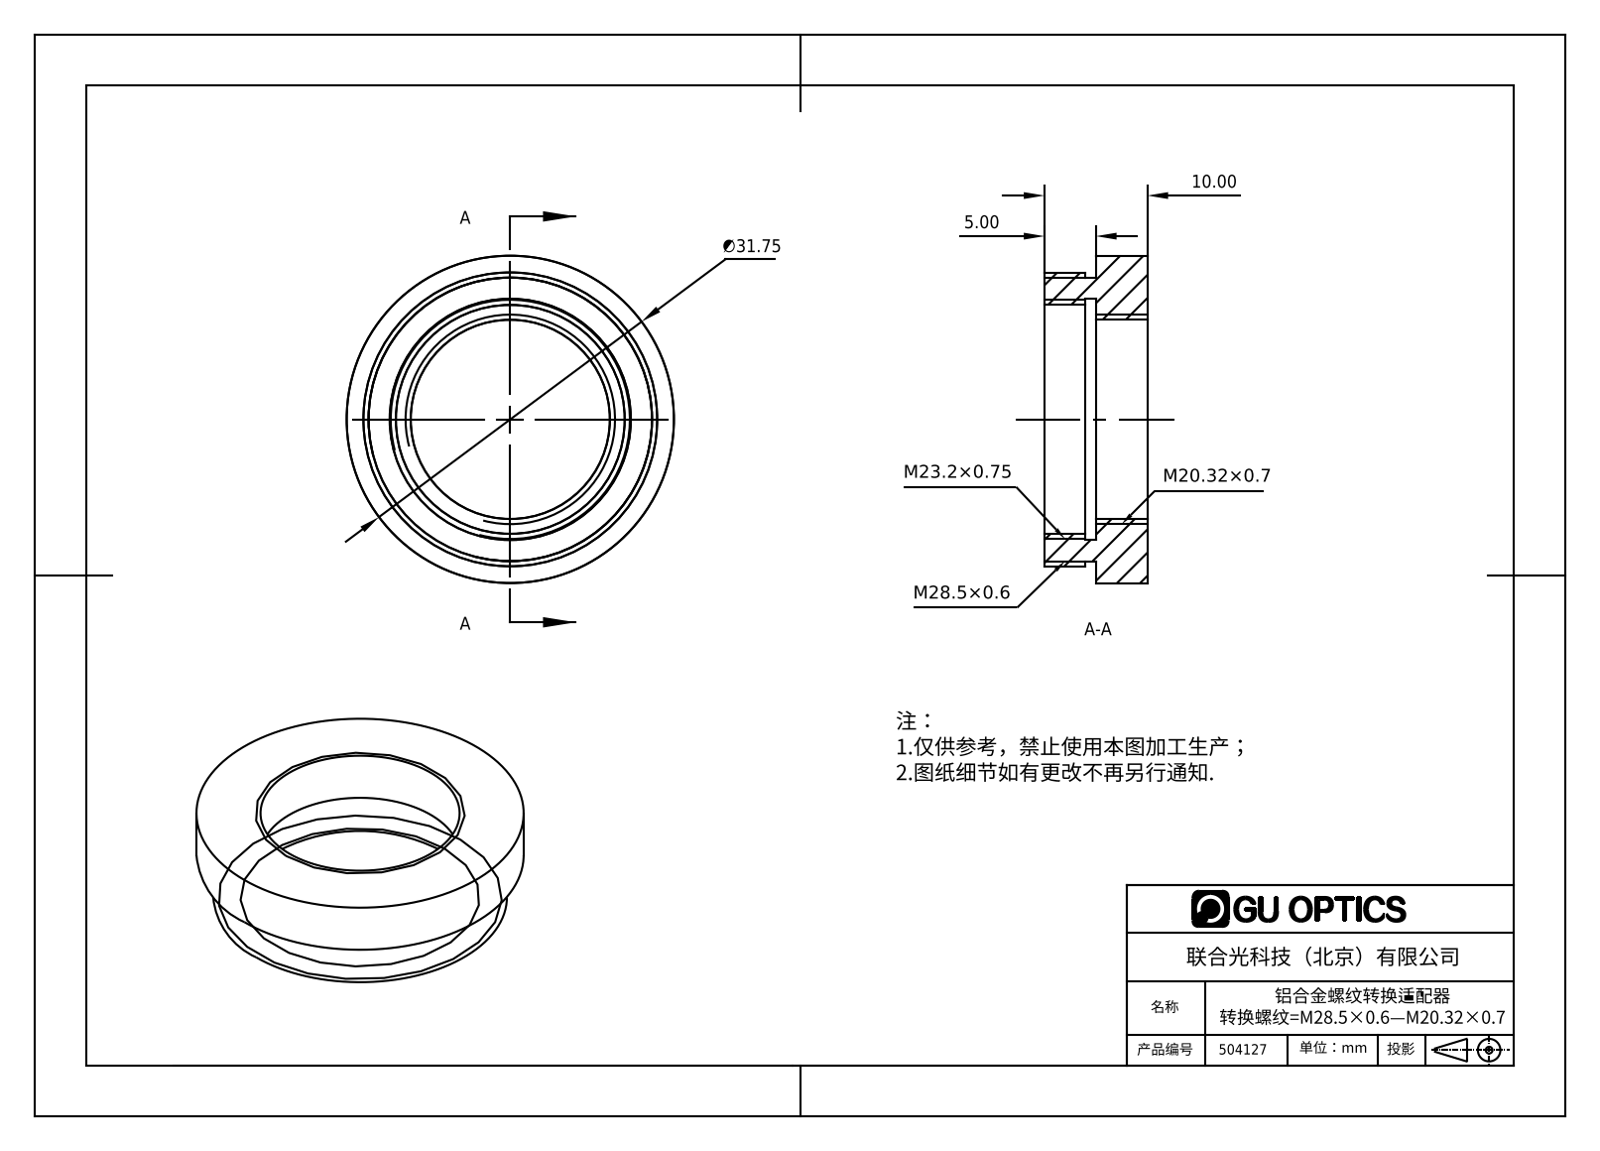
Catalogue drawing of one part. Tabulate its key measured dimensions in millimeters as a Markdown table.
| quantity | value |
| --- | --- |
| part name | 504127 |
| STEP written by | SolidWorks 2016 (AUTOMOTIVE_DESIGN) |
| units | millimeters |
| bodies | 1 solid, 18 faces (6 planar, 12 cylindrical, 0 other) |
| overall size | 31.75 × 31.75 × 10 |
| volume | 3 660 mm³ |
| surface area | 2 770 mm² |
| round holes (diameter × count) | 19.32 × 1, 22.2 × 1, 23.4 × 1 |
| round bosses / shafts (diameter × count) | 31.75 × 1, 28.5 × 1, 27.5 × 1 |
| main face-to-face distances | 5, 10, 4, 1, 6 |
